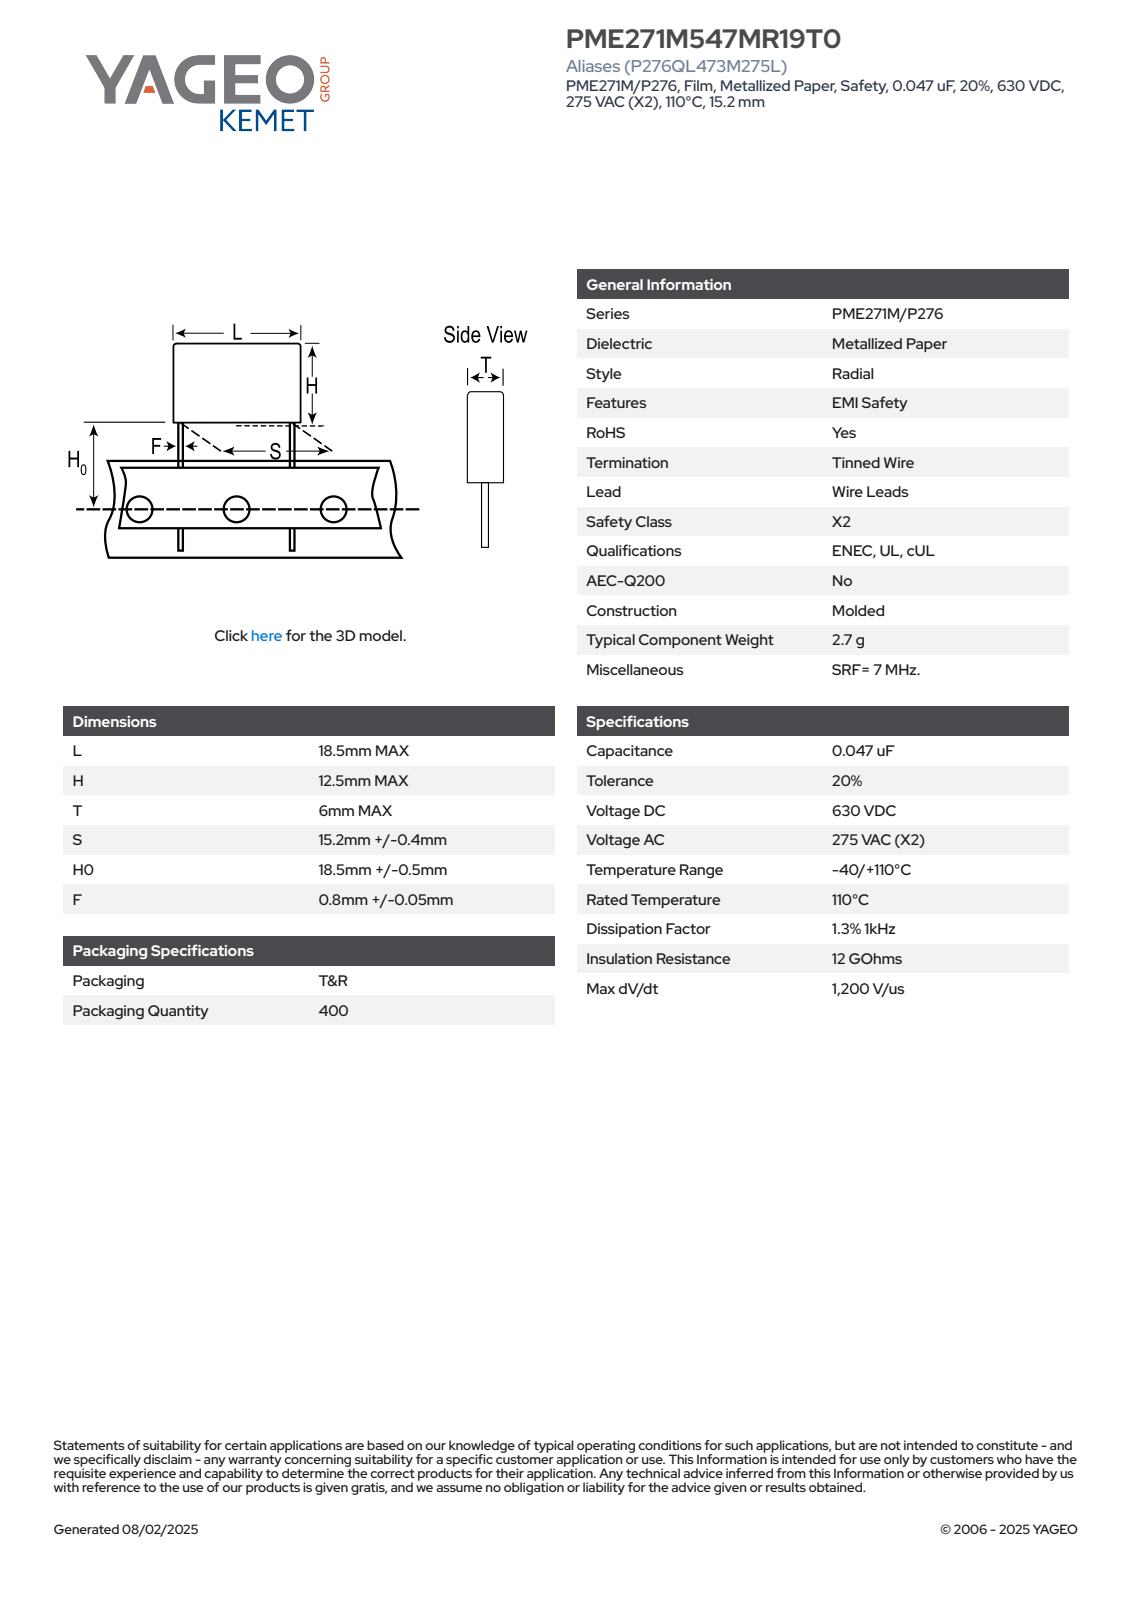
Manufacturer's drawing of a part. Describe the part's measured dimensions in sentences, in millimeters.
The part is named "CFR_MOLDED_18.5X12.5X6_L18.5H12.5T6S15.2H019F0.8". Its 3-D file was written by "SolidWorks 2014 (AUTOMOTIVE_DESIGN)". It is 4 solids with 73 faces: 65 planar, 8 cylindrical and 0 other. Overall it measures 31.5 by 18.5 by 6 millimeters. Its volume is 1 404 cubic millimeters and its surface area 936 square millimeters. Round bosses or shafts: 2 of diameter 0.8. Partial cylindrical surfaces (rounded edges, fillets, slot ends): 4 of radius 0.5. The main face-to-face distances are 6, 12.5, 18.5, 19, 31.5, 25.9, 6.9, 5.6, 24.24, 5.24.
